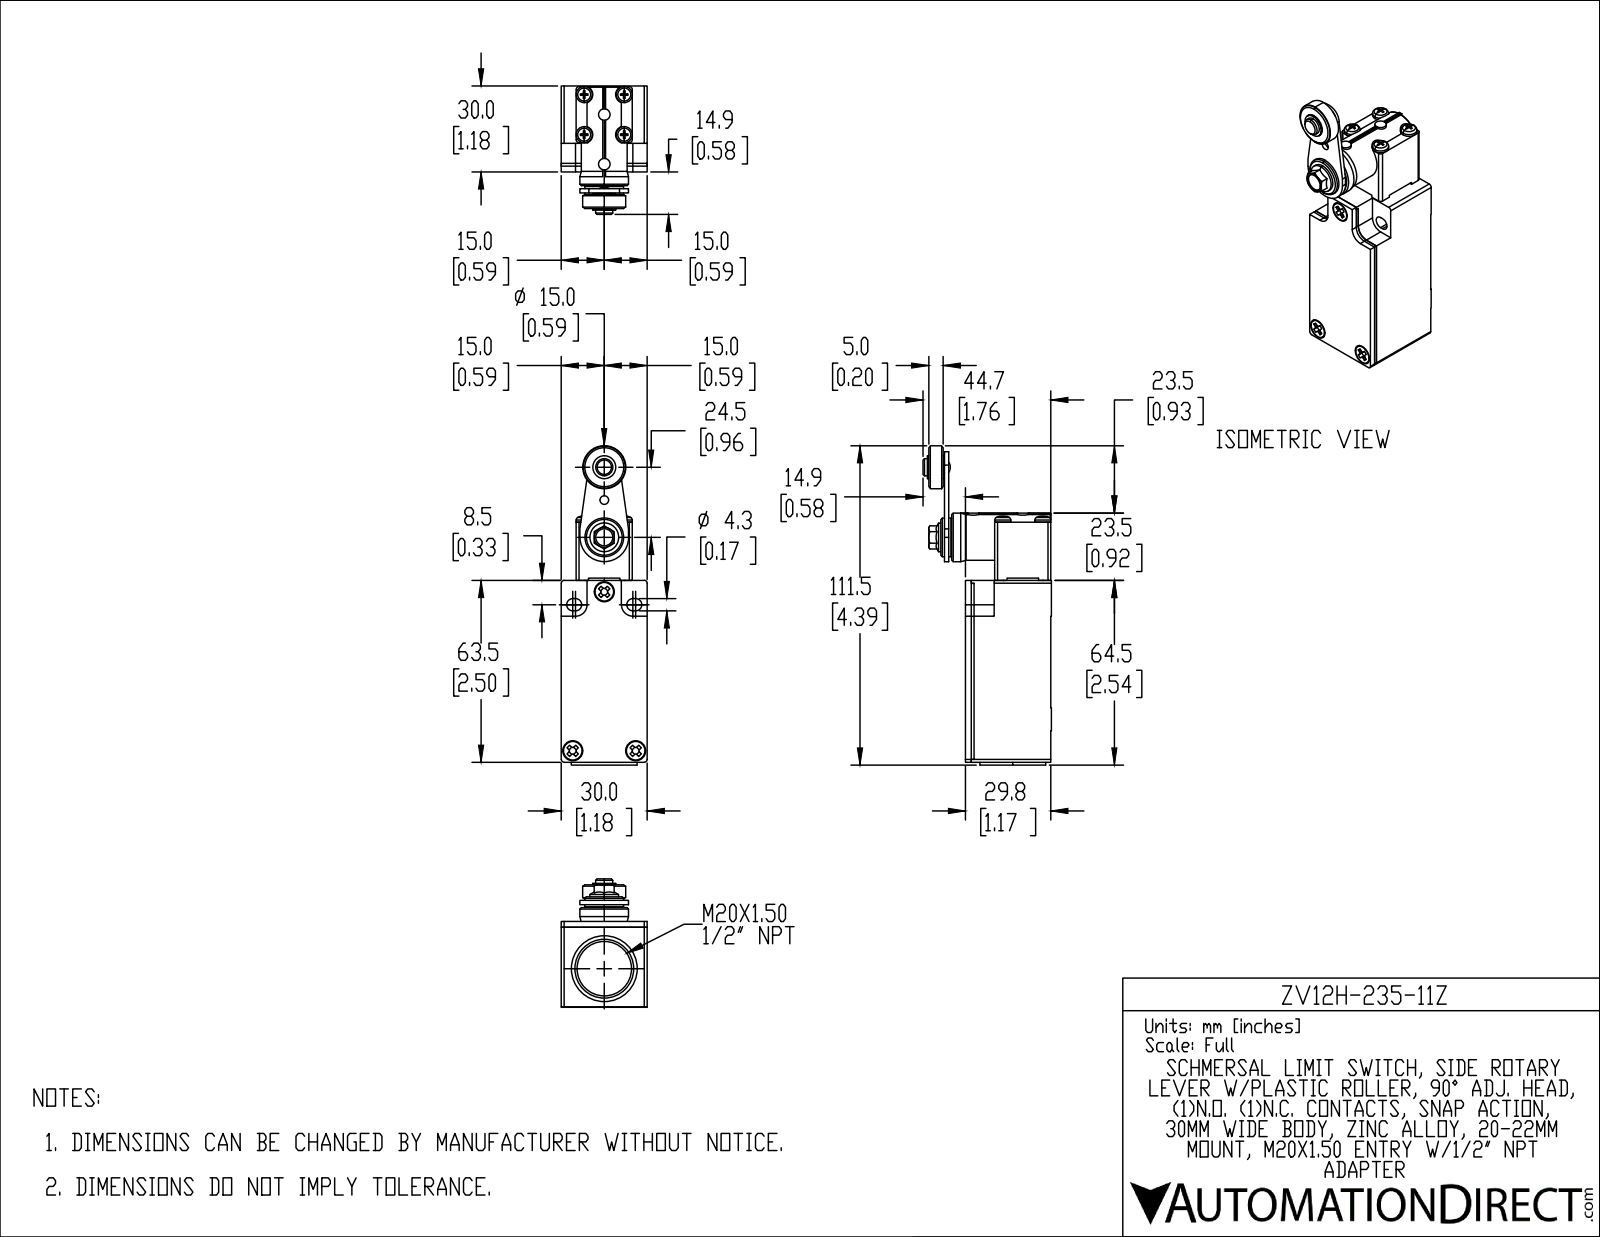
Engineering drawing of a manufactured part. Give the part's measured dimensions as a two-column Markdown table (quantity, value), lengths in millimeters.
| quantity | value |
| --- | --- |
| part name | ZV12H-235-11Z |
| STEP written by | SolidWorks 2019 (AUTOMOTIVE_DESIGN) |
| units | millimeters |
| bodies | 1 solid, 455 faces (268 planar, 139 cylindrical, 48 other) |
| overall size | 111.5 × 44.9 × 30 |
| volume | 65 660 mm³ |
| surface area | 16 300 mm² |
| round holes (diameter × count) | 2.4 × 4, 3.2 × 4, 7 × 3, 3 × 1, 6 × 1, 13 × 1, 13.8 × 1, 19 × 1 |
| round bosses / shafts (diameter × count) | 5.6 × 4, 5.4 × 4, 6.5 × 3, 4 × 3, 23 × 1, 17 × 1, 16 × 1, 15 × 1 |
| partial cylindrical surfaces (radius × count) | 0.5 × 12, 1 × 8, 1.5 × 4, 2.2 × 4, 3 × 4, 4 × 2, 4 × 2, 0.2 × 1 |
| main face-to-face distances | 30, 29.8, 5.2, 24.8, 19.6, 63.5, 5.8, 35.7, 35.8, 19.8 |
| hole center spacings | 9.9, 14, 7.8, 12.6, 19.8, 56.6, 75.3, 88.2 |
